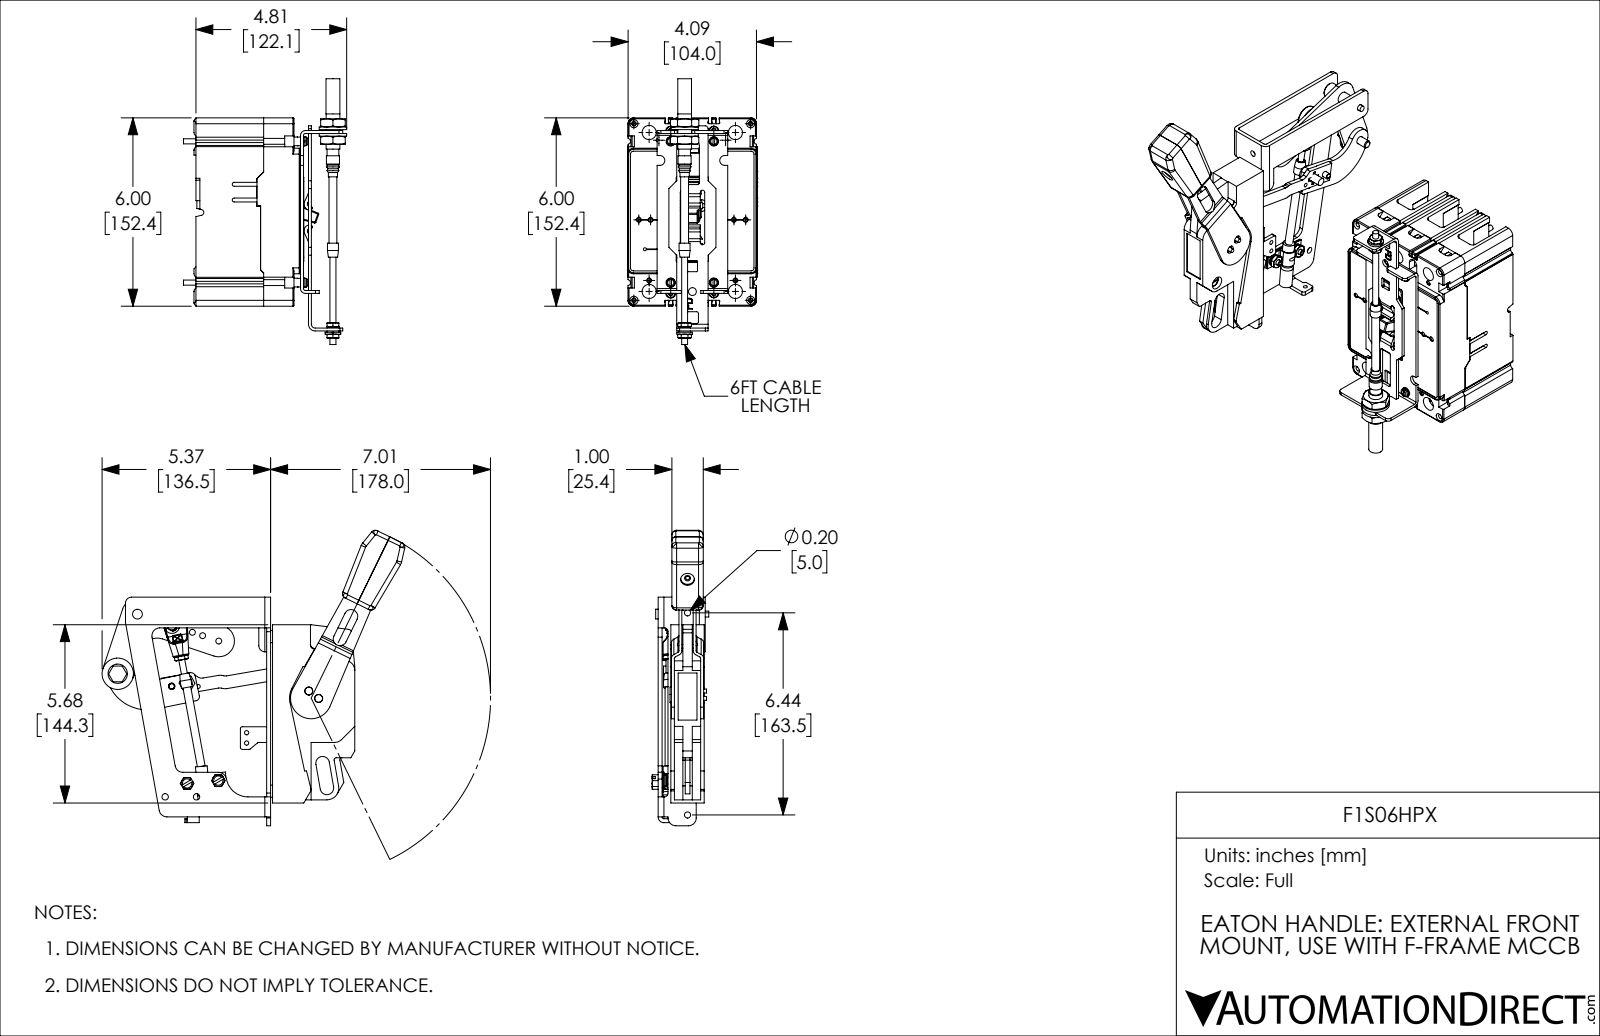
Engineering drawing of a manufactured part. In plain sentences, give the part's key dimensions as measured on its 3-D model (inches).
The part is named "F1S06HPX; F1S06HPX_BREAKER; F1S06HPX_HANDLE". Its 3-D file was written by "SolidWorks 2019 (CONFIG_CONTROL_DESIGN)". It is 82 solids with 4453 faces: 2368 planar, 1637 cylindrical and 448 other. Overall it measures 10.091 by 9.783 by 9.651 inches. Its volume is 47.35 cubic inches and its surface area 700.7 square inches. Round holes: 12 of diameter 0.156, 11 of diameter 0.188, 8 of diameter 0.114, 8 of diameter 0.16, 6 of diameter 0.125, 6 of diameter 0.136, 6 of diameter 0.141, 6 of diameter 0.145, 6 of diameter 0.168, 6 of diameter 0.203, 6 of diameter 0.45, 5 of diameter 0.11. Round bosses or shafts: 8 of diameter 0.25, 6 of diameter 0.297, 6 of diameter 0.164, 4 of diameter 0.418, 4 of diameter 0.375, 4 of diameter 0.281, 4 of diameter 0.27, 4 of diameter 0.219. Partial cylindrical surfaces (rounded edges, fillets, slot ends): 115 of radius 0.031, 67 of radius 0.06, 56 of radius 0.062, 56 of radius 0.125, 50 of radius 0.03, 38 of radius 0.032, 33 of radius 0.09, 23 of radius 0.12. The main face-to-face distances are 0.125, 0.125, 0.187, 0.094, 0.247, 0.11, 0.95, 0.117, 2.126, 0.218. The hole center spacings are 4.83, 0.742, 1.375, 4.5, 0.344, 0.691, 0.743, 2.082.
